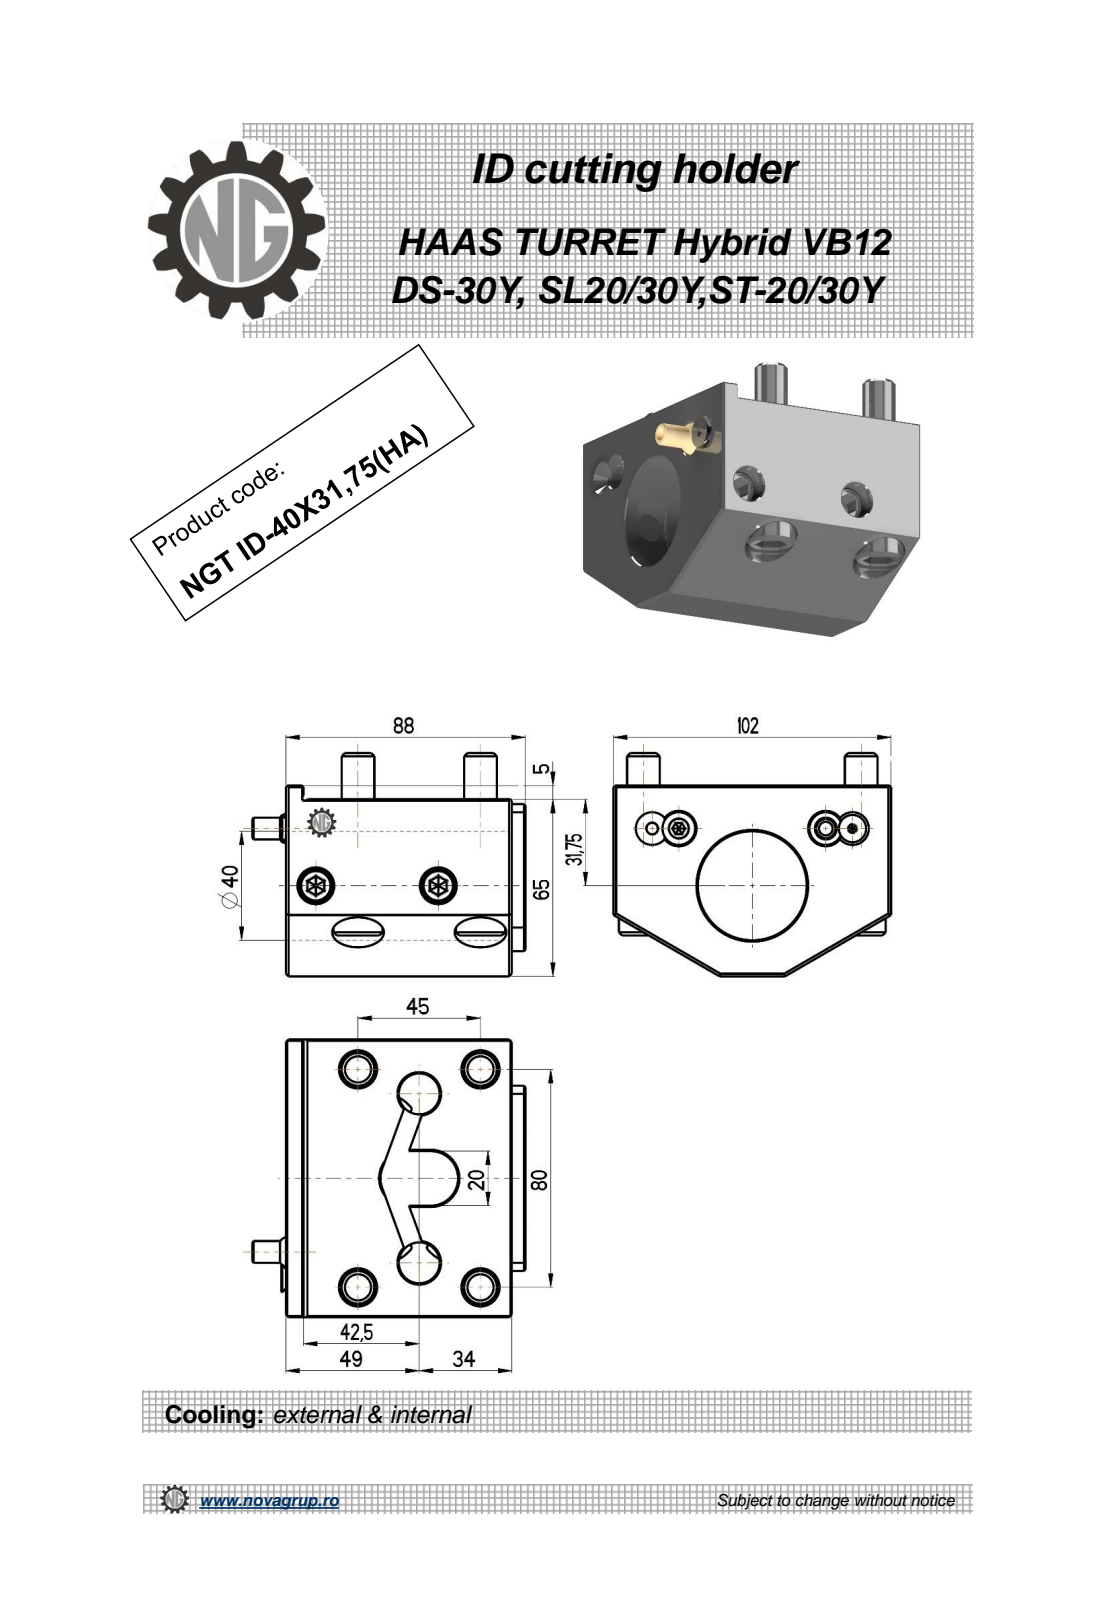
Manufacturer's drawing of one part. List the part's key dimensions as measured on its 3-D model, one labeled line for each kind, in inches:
Part name (STEP PRODUCT): NGT_ID_40_31_75_HA
STEP written by: PRO/ENGINEER BY PARAMETRIC TECHNOLOGY CORPORATION, 2010280 (CONFIG_CONTROL_DESIGN)
Units: inches
Bodies: 1 solid, 295 faces (128 planar, 93 cylindrical, 74 other)
Overall size (bounding box): 4.016 × 3.95 × 3.228
Volume: 23.7 in³ · Surface area: 88.21 in²
Round holes (diameter × count): ⌀0.402 ×2, ⌀0.492 ×2, ⌀0.591 ×2, ⌀0.197 ×1, ⌀1.575 ×1
Round bosses / shafts (diameter × count): ⌀0.472 ×6, ⌀0.394 ×1, ⌀0.315 ×1
Partial cylindrical surfaces — rounded edges, fillets, slot ends (radius × count): R0.024 ×24, R0.014 ×12, R0.008 ×6, R0.354 ×4, R0.394 ×2, R0.039 ×1
Main face-to-face distances: 0.197, 3.465, 3.268, 4.016, 2.559, 2.362, 0.669, 0.394, 2.756, 2.165
Hole centre spacings: 1.347, 1.772, 2.441
